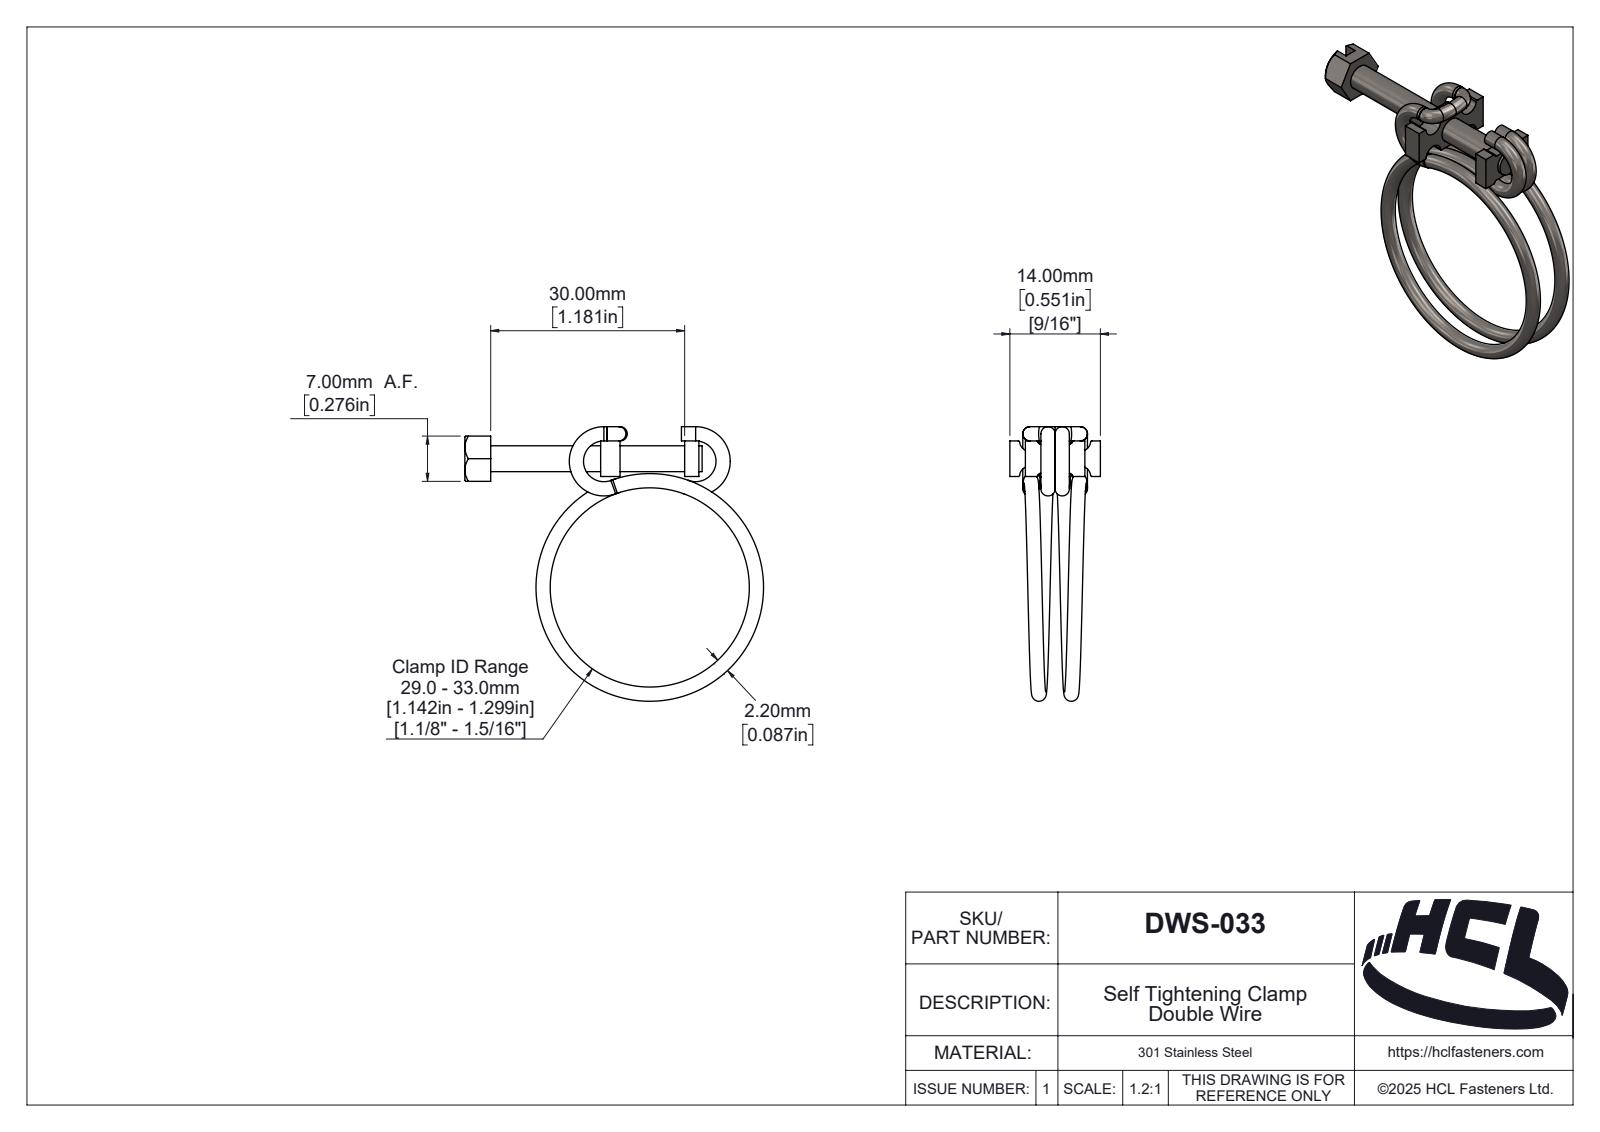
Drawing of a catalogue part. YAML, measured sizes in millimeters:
part_name: "DWS-033"
step_written_by: "SolidWorks 2025 (AUTOMOTIVE_DESIGN)"
units: millimeters
bodies: {solids: 6, faces: 209, planar: 51, cylindrical: 74, other: 84}
overall_size: [46.2, 42.45, 14]
volume: 1929
surface_area: 3173
round_holes:
  - {diameter: 4, count: 1}
round_bosses_or_shafts:
  - {diameter: 2.2, count: 4}
partial_cylinders:
  - {radius: 0.2, count: 12}
  - {radius: 0.5, count: 4}
  - {radius: 1.6, count: 4}
  - {radius: 0.4, count: 1}
  - {radius: 0.51, count: 1}
  - {radius: 0.53, count: 1}
  - {radius: 0.64, count: 1}
  - {radius: 0.91, count: 1}
face_to_face_distances: [2, 3, 20, 7, 0.5, 13, 10, 15.2, 12.2, 2.2]
